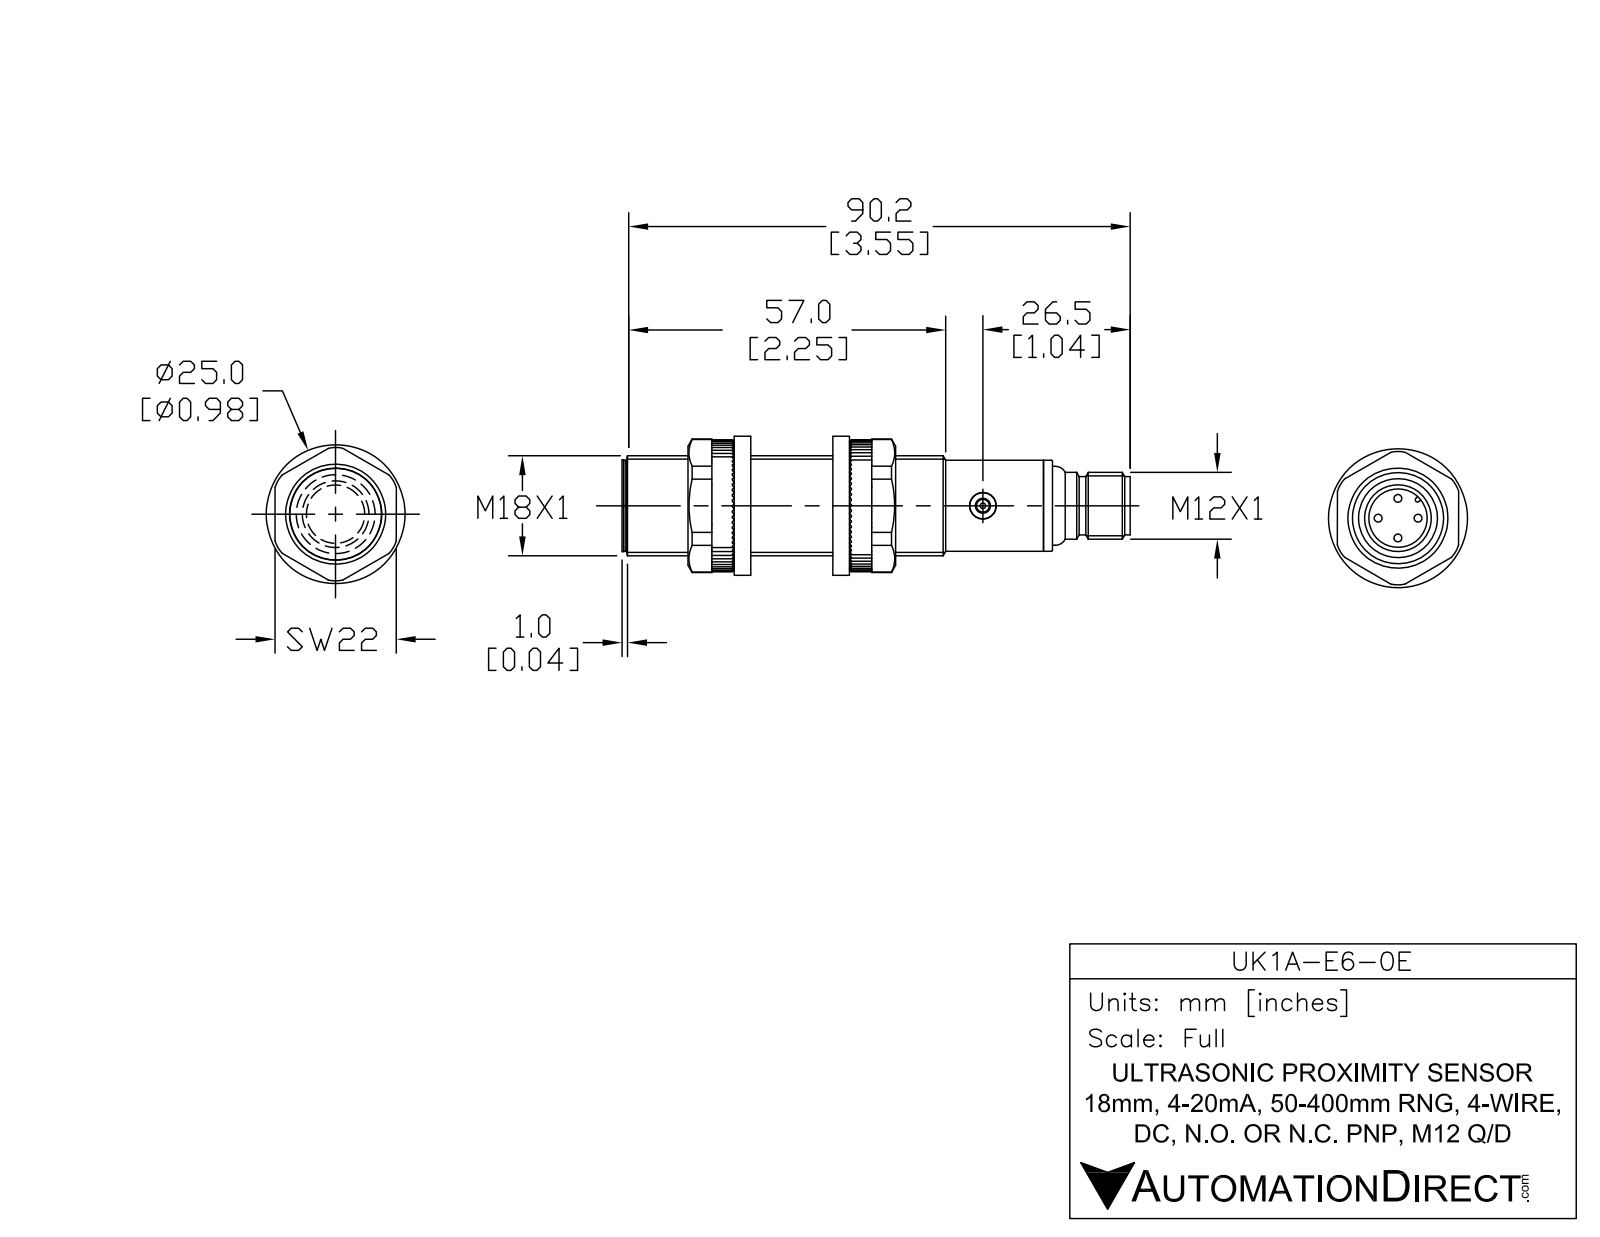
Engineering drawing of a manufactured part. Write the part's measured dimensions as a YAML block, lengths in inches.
part_name: "UK1A-E6-0E"
step_written_by: "SolidWorks 2017 (AUTOMOTIVE_DESIGN)"
units: inches
bodies: {solids: 6, faces: 106, planar: 21, cylindrical: 48, other: 37}
overall_size: [3.606, 0.709, 0.709]
volume: 1.202
surface_area: 10.68
round_holes:
  - {diameter: 0.106, count: 1}
  - {diameter: 0.185, count: 1}
  - {diameter: 0.276, count: 1}
  - {diameter: 0.327, count: 1}
  - {diameter: 0.374, count: 1}
round_bosses_or_shafts:
  - {diameter: 0.039, count: 4}
  - {diameter: 0.709, count: 1}
  - {diameter: 0.654, count: 1}
  - {diameter: 0.646, count: 1}
  - {diameter: 0.622, count: 1}
  - {diameter: 0.559, count: 1}
  - {diameter: 0.472, count: 1}
  - {diameter: 0.413, count: 1}
partial_cylinders:
  - {radius: 0.024, count: 1}
face_to_face_distances: [2.957, 0.039, 2.996, 0.037, 2.994, 0.043, 0.157, 3.055, 3.053, 3.016]
